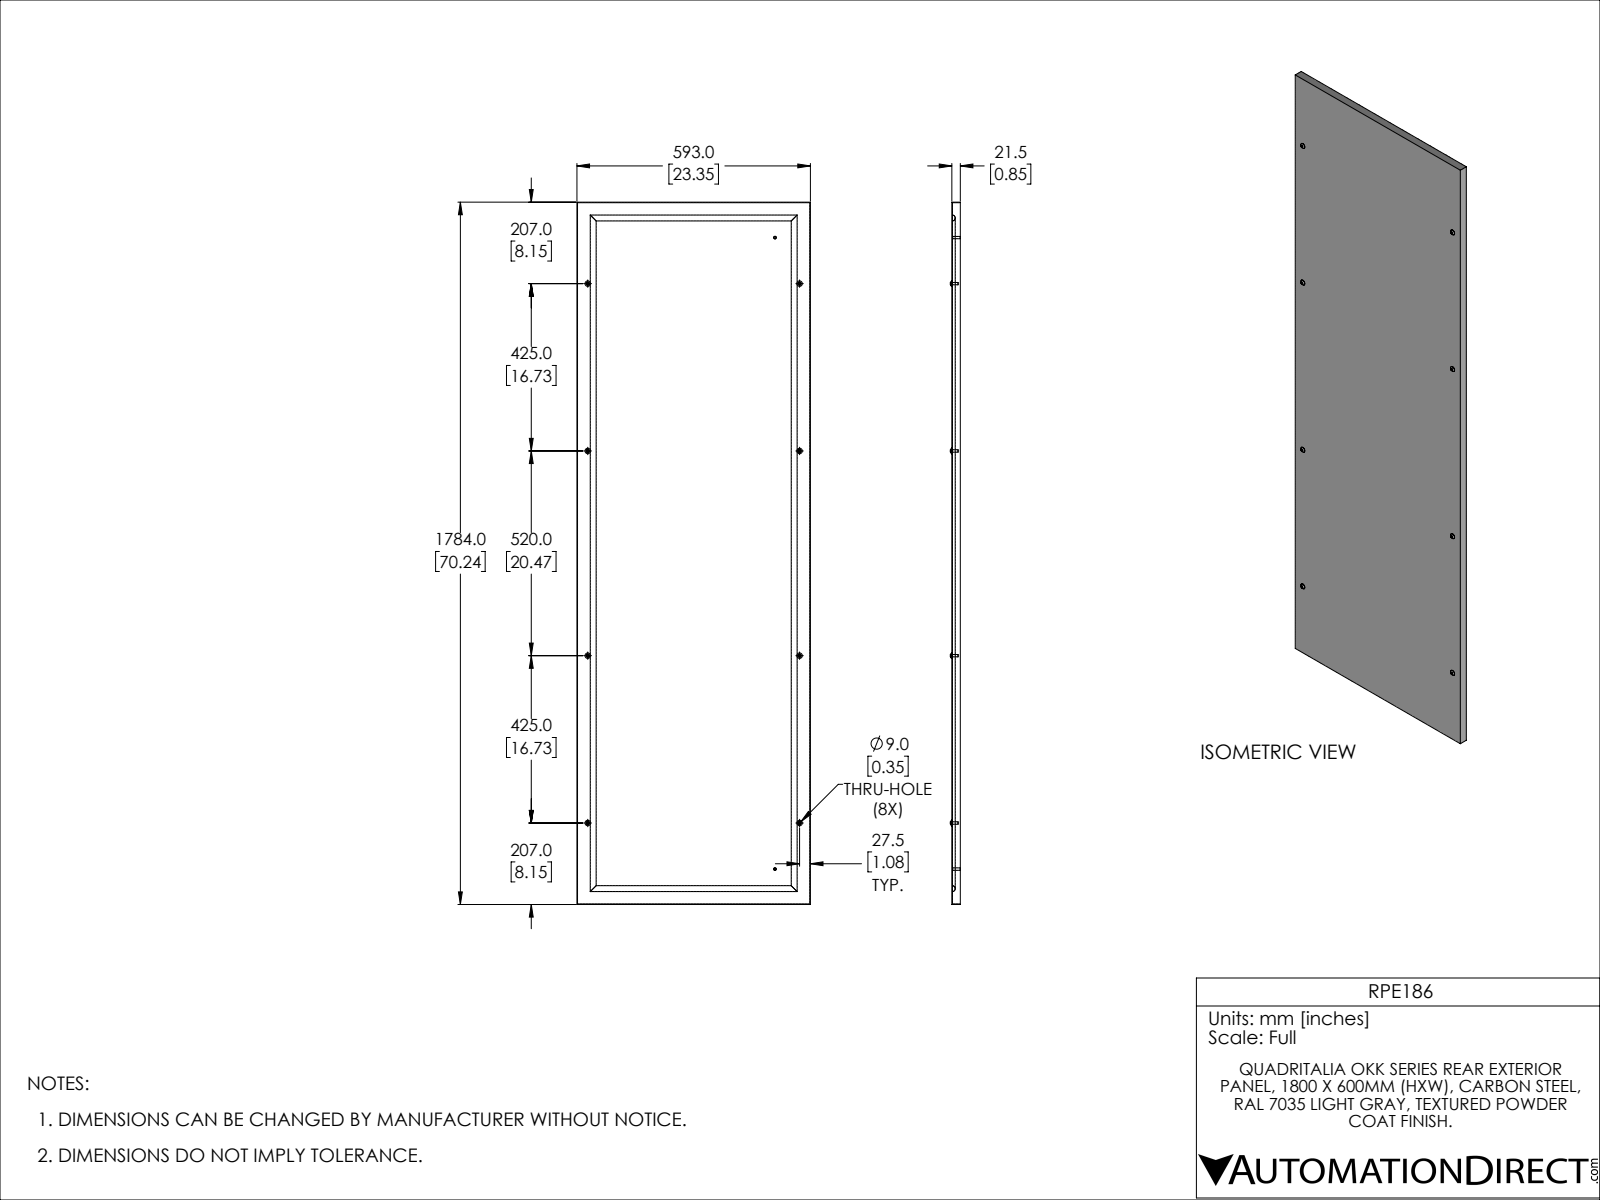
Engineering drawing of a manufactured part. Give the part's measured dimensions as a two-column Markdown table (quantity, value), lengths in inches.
| quantity | value |
| --- | --- |
| part name | RPE186 |
| STEP written by | SolidWorks 2021 (CONFIG_CONTROL_DESIGN) |
| units | inches |
| bodies | 15 solids, 311 faces (157 planar, 128 cylindrical, 26 other) |
| overall size | 70.236 × 23.346 × 0.992 |
| volume | 127.8 in³ |
| surface area | 3 853 in² |
| round holes (diameter × count) | 0.354 × 8 |
| round bosses / shafts (diameter × count) | 0.236 × 10, 0.551 × 8, 0.276 × 2 |
| partial cylindrical surfaces (radius × count) | 0.02 × 96, 0.296 × 4 |
| main face-to-face distances | 0.059, 23.287, 23.346, 23.228, 70.177, 70.236, 70.118, 0.846, 0.787, 33.207 |
| hole center spacings | 16.732, 21.181, 26.993, 37.205, 42.811, 20.472, 29.458, 53.937 |
